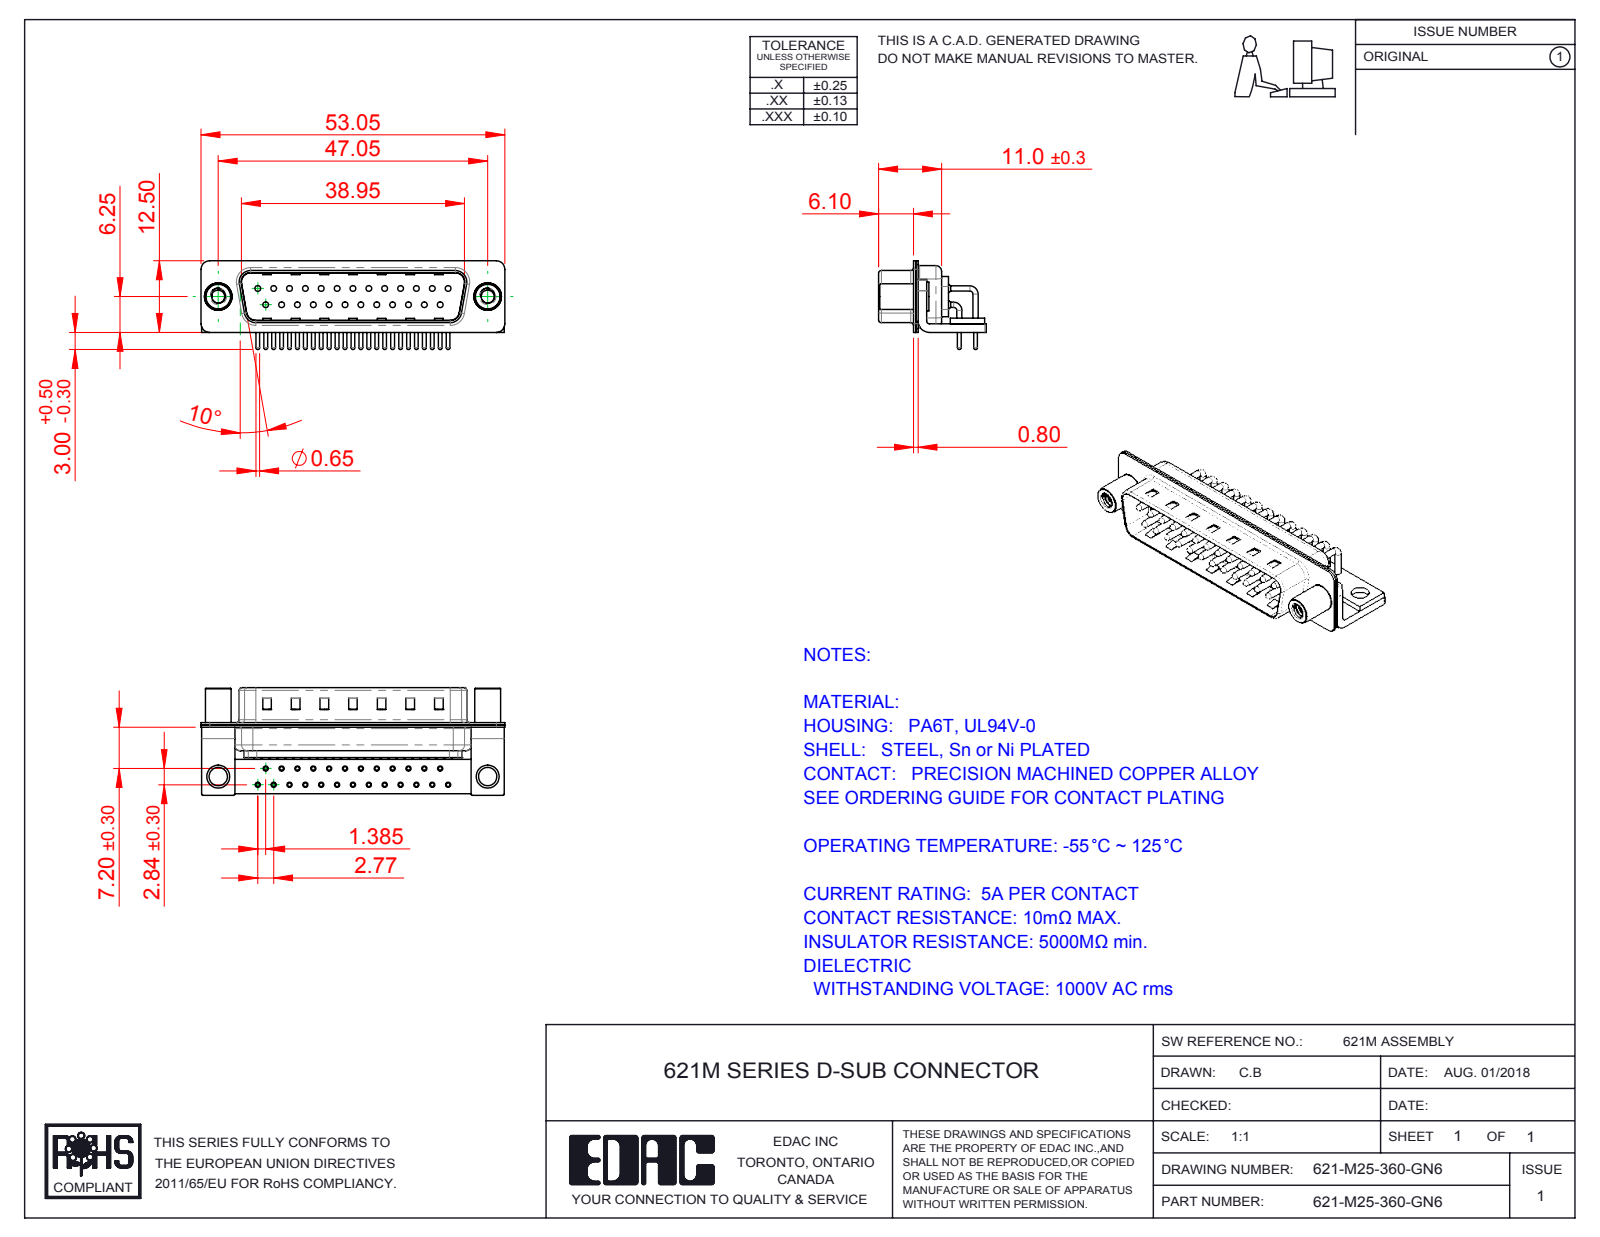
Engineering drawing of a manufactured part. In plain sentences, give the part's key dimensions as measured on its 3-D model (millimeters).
The part is named "621-M25-360-GN6; 621M Stabilizer Bracket; 621M Shell Rear_25 Contacts; 621M Housing_25 Contacts (+5 more)". Its 3-D file was written by "SolidWorks 2016 (CONFIG_CONTROL_DESIGN)". It is 33 solids with 3276 faces: 1799 planar, 1151 cylindrical and 326 other. Overall it measures 53.05 by 18.8 by 15.49 millimeters. Its volume is 3 511 cubic millimeters and its surface area 9 207 square millimeters. Round holes: 25 of diameter 0.9, 25 of diameter 1, 25 of diameter 1.7, 25 of diameter 2, 2 of diameter 2.26, 2 of diameter 3.2, 2 of diameter 4, 2 of diameter 4.8. Round bosses or shafts: 33 of diameter 0.9, 25 of diameter 1.5, 25 of diameter 0.65, 2 of diameter 5, 2 of diameter 4.9, 2 of diameter 4.5. Partial cylindrical surfaces (rounded edges, fillets, slot ends): 25 of radius 1.01, 16 of radius 0.25, 16 of radius 1.5, 13 of radius 2, 9 of radius 0.5, 8 of radius 1.6, 4 of radius 0.6, 4 of radius 0.65. The main face-to-face distances are 0.4, 0.85, 1.25, 1.5, 9.55, 0.8, 10.4, 8.3, 1, 1.9. The hole center spacings are 3.16, 2.77, 8.31, 5.54, 11.08, 13.85, 5.04, 16.62.
